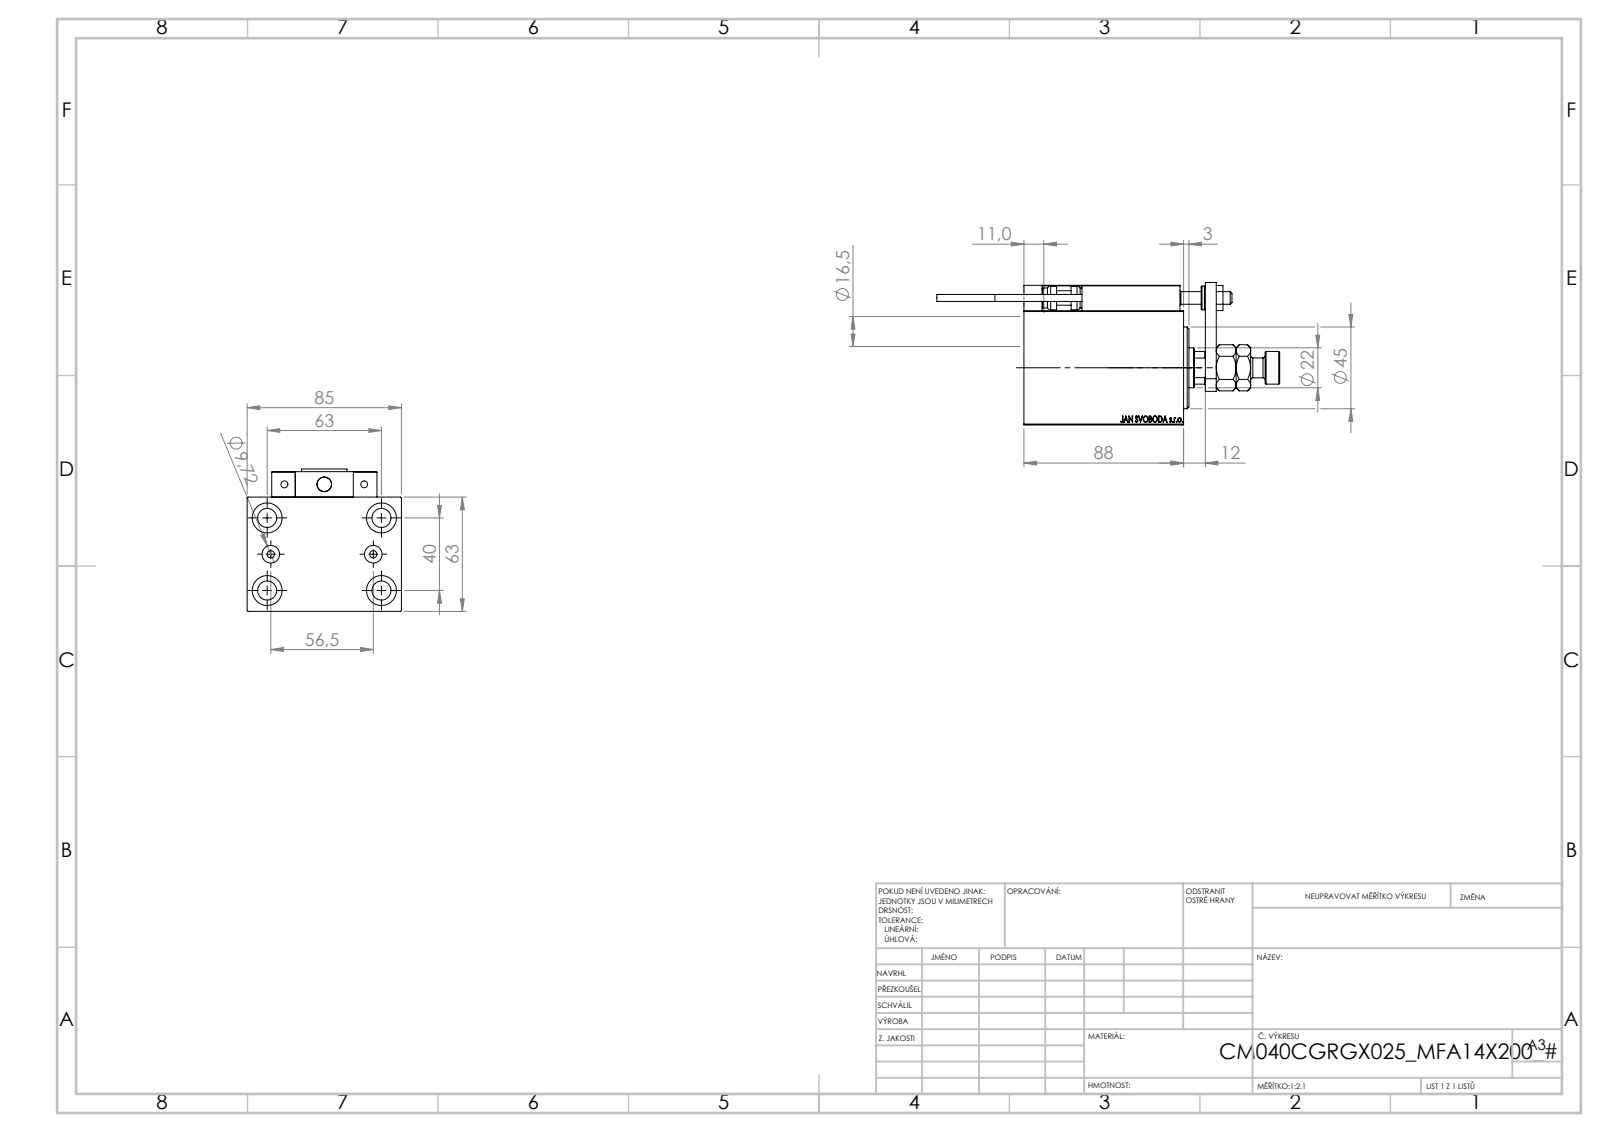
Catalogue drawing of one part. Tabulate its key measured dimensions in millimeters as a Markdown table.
| quantity | value |
| --- | --- |
| part name | KONCOVKA; Block; V450CM_C_Body; ZARAZKA (+8 more) |
| STEP written by | SolidWorks 2019 (CONFIG_CONTROL_DESIGN) |
| units | millimeters |
| bodies | 24 solids, 1330 faces (576 planar, 188 cylindrical, 566 other) |
| overall size | 189 × 85 × 78.5 |
| volume | 468 554 mm³ |
| surface area | 108 759 mm² |
| round holes (diameter × count) | 4 × 6, 8 × 5, 16.5 × 5, 3.2 × 4, 10.5 × 4, 5 × 2, 9.72 × 2, 7 × 1, 12.5 × 1, 22 × 1, 25.5 × 1, 40 × 1 |
| round bosses / shafts (diameter × count) | 11 × 2, 5 × 2, 3.8 × 2, 18 × 1, 13 × 1 |
| partial cylindrical surfaces (radius × count) | 0.3 × 30, 3 × 2, 10.5 × 1 |
| main face-to-face distances | 63, 85, 12, 88, 76, 14, 77, 18, 25, 20 |
| hole center spacings | 20.26, 37.31, 63.01, 11.37, 20, 28.25, 29.59, 29.69 |
